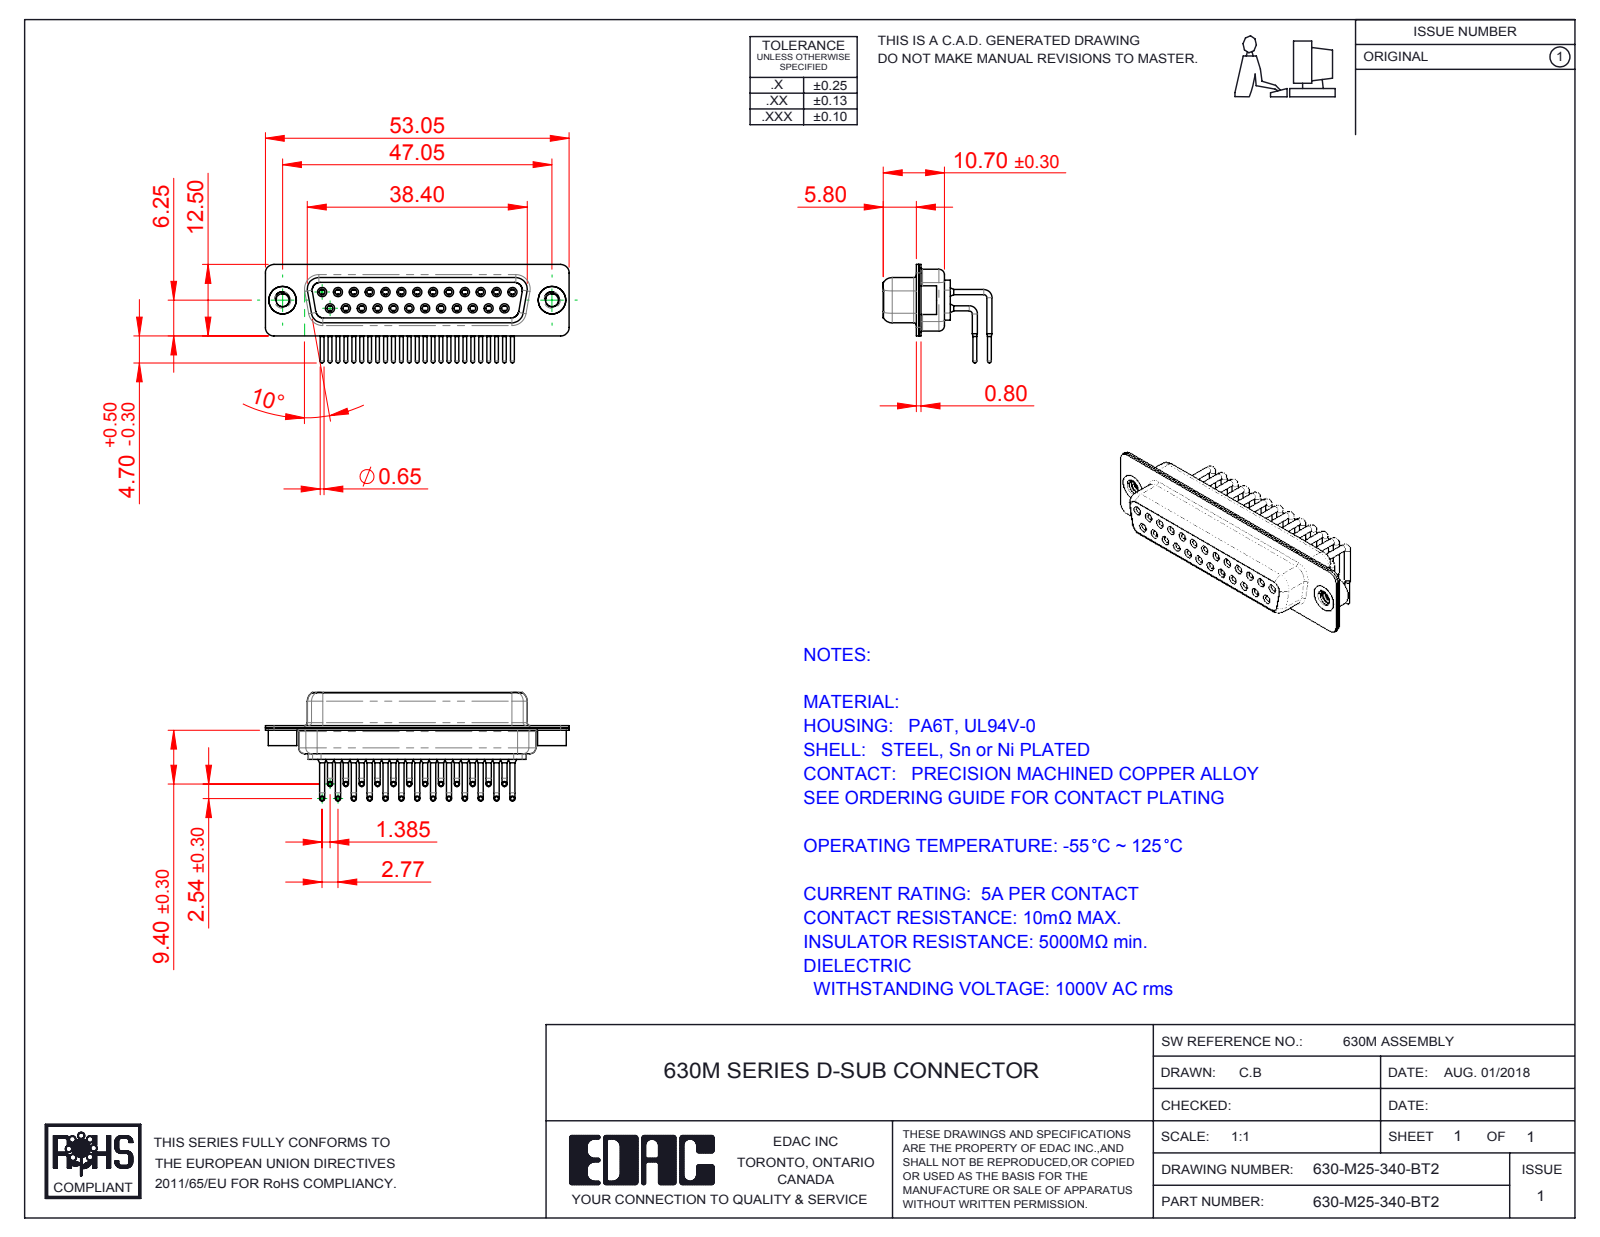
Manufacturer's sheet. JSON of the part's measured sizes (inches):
{"part_name": "630M Shell Rear_25 Contacts; 630-M25-340-BT2; 630M Contact Row 2; 630M 4-40 Threaded Rivet (+3 more)", "step_written_by": "SolidWorks 2016 (CONFIG_CONTROL_DESIGN)", "units": "inches", "bodies": {"solids": 30, "faces": 1604, "planar": 442, "cylindrical": 712, "other": 450}, "overall_size": [2.089, 0.748, 0.677], "volume_in3": 0.238, "surface_area_in2": 15.08, "round_holes": [[0.039, 25], [0.043, 25], [0.067, 25], [0.071, 25], [0.079, 25], [0.089, 2], [0.157, 2], [0.189, 2]], "round_bosses_or_shafts": [[0.035, 50], [0.063, 25], [0.059, 25], [0.026, 25], [0.197, 2], [0.193, 2]], "partial_cylinders_radius": [[0.059, 16], [0.079, 12], [0.053, 10], [0.063, 8], [0.01, 4], [0.02, 4], [0.024, 4], [0.026, 4]], "face_to_face_distances": [0.016, 0.057, 0.352, 0.244, 0.091, 0.075, 0.335, 0.278, 0.018, 0.033], "hole_center_spacings": [0.124, 0.109, 0.218, 0.327, 0.436, 0.545, 0.198, 0.295]}
